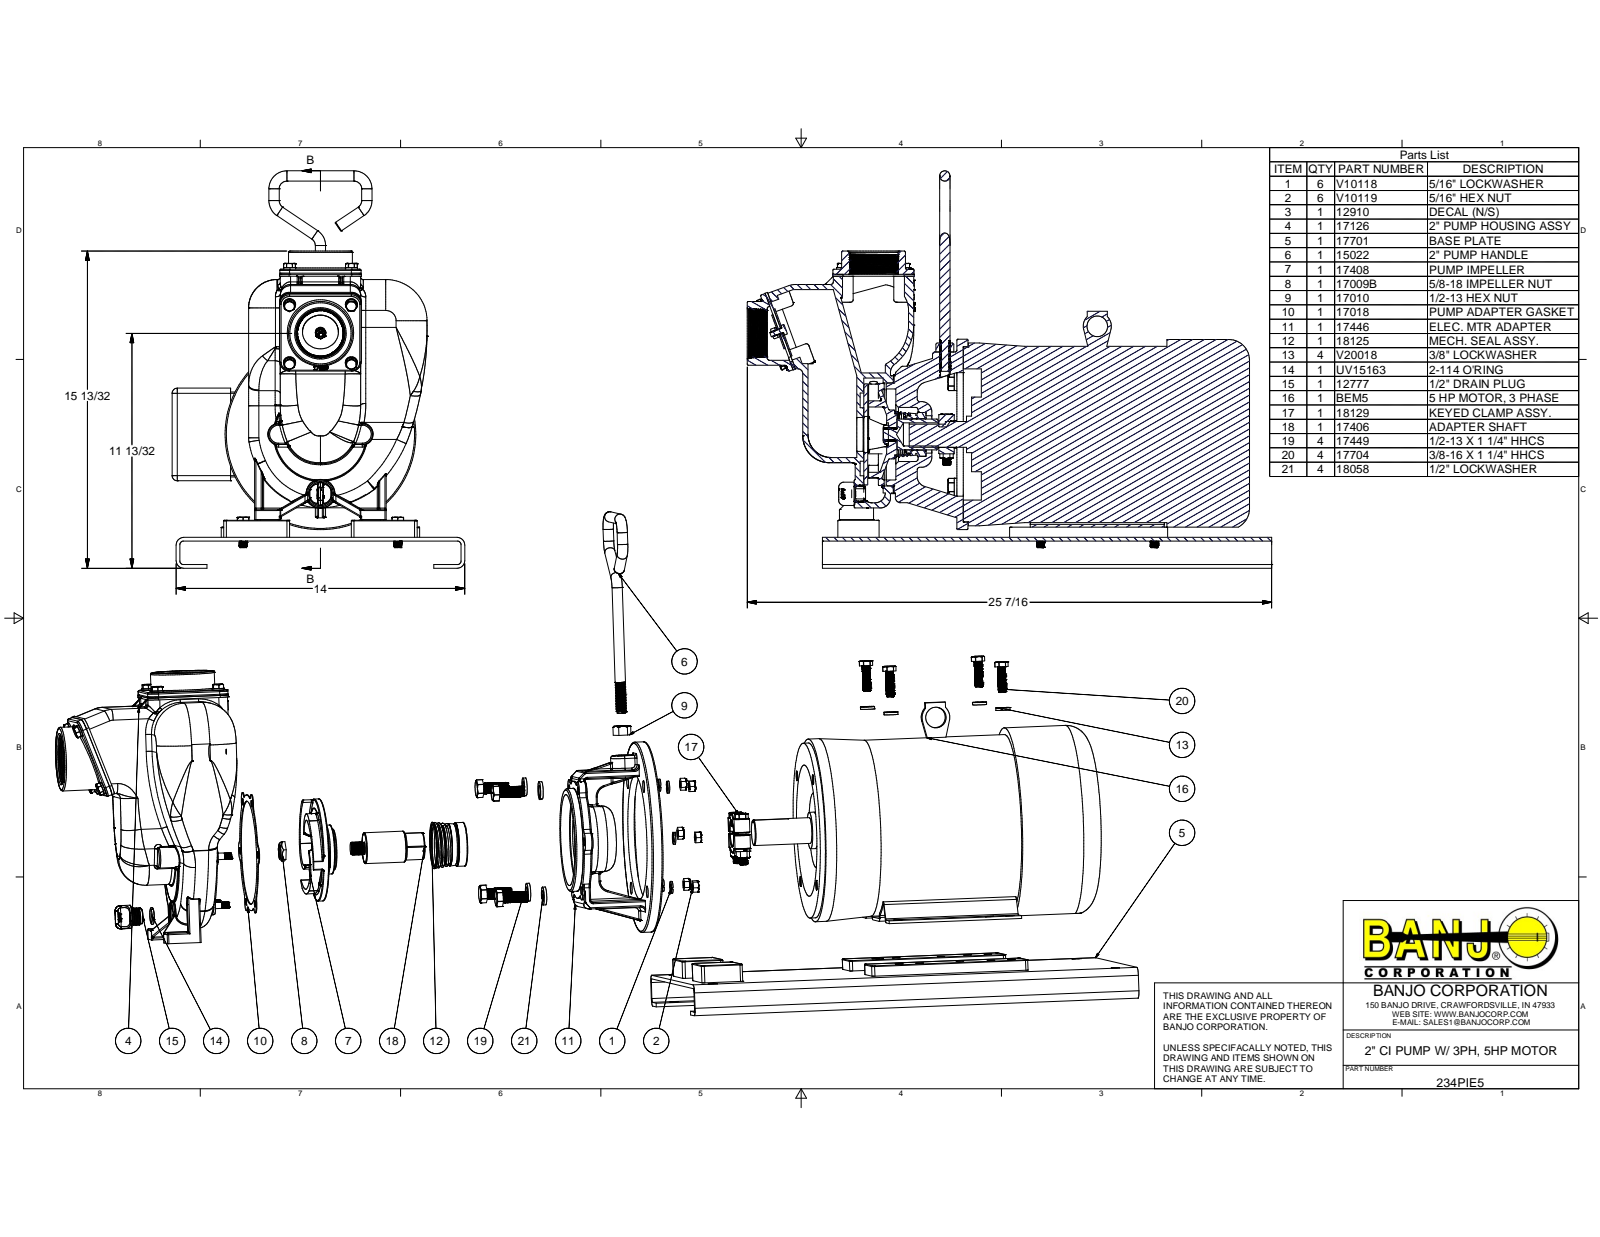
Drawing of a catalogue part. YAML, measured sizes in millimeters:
part_name: "234PIE5; 17126; 17026; 17000 (+8 more)"
step_written_by: "Autodesk Inventor 2013 (AUTOMOTIVE_DESIGN)"
units: millimeters
bodies: {solids: 89, faces: 6834, planar: 1227, cylindrical: 2490, other: 3117}
overall_size: [646.2, 490.3, 360.5]
volume: 18930000
surface_area: 1909000
round_holes:
  - {diameter: 6.4, count: 17}
  - {diameter: 8.2, count: 14}
  - {diameter: 7.8, count: 12}
  - {diameter: 10.4, count: 10}
  - {diameter: 8, count: 8}
  - {diameter: 8.7, count: 8}
  - {diameter: 6.4, count: 6}
  - {diameter: 9.5, count: 6}
  - {diameter: 9.8, count: 6}
  - {diameter: 10.6, count: 5}
  - {diameter: 13, count: 4}
  - {diameter: 14.3, count: 4}
round_bosses_or_shafts:
  - {diameter: 6.8, count: 132}
  - {diameter: 8.2, count: 106}
  - {diameter: 11.1, count: 60}
  - {diameter: 14.8, count: 14}
  - {diameter: 5.4, count: 12}
  - {diameter: 8, count: 10}
  - {diameter: 12.7, count: 9}
  - {diameter: 17.4, count: 6}
partial_cylinders:
  - {radius: 1.5, count: 84}
  - {radius: 0.8, count: 74}
  - {radius: 6.4, count: 66}
  - {radius: 3.2, count: 57}
  - {radius: 2.3, count: 29}
  - {radius: 12.7, count: 24}
  - {radius: 1.6, count: 20}
  - {radius: 11.9, count: 16}
face_to_face_distances: [4.5, 33.6, 12.7, 17.2, 38.1, 6.4, 29, 46.3, 50.8, 7.9]
hole_center_spacings: [76.2, 53.9, 71.5, 53.9, 107.8, 130.4, 107.8, 123.7]
